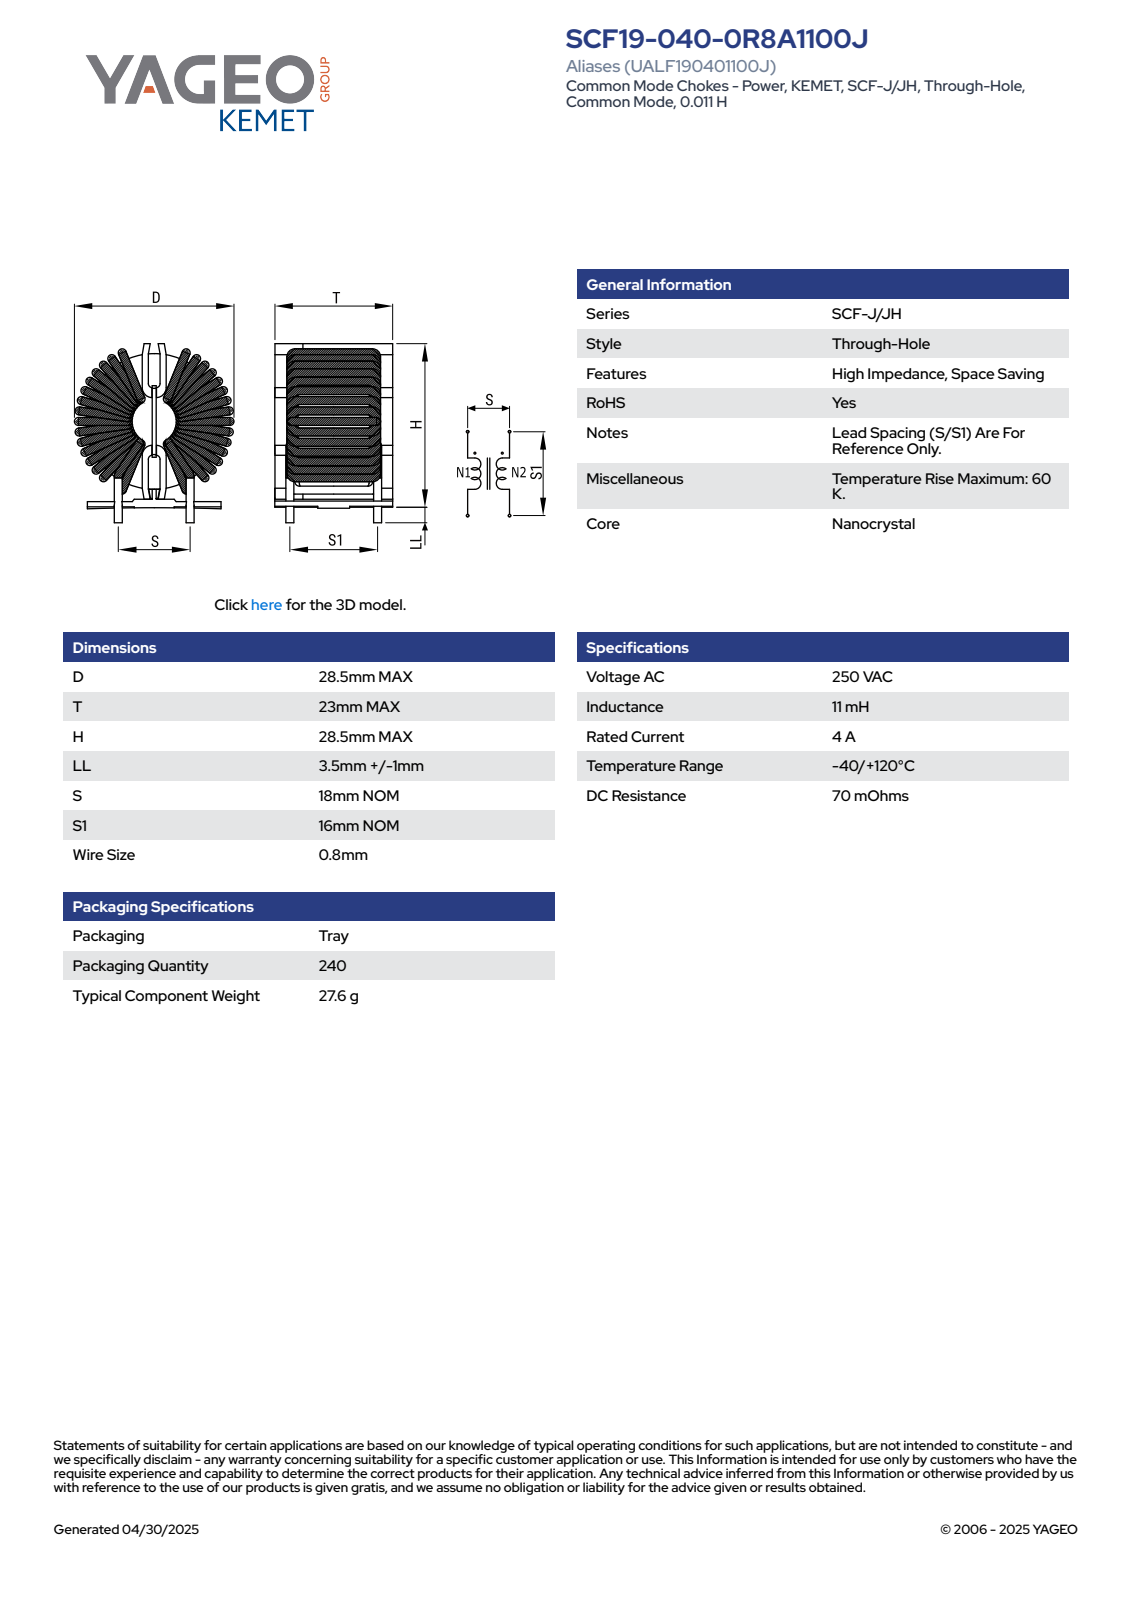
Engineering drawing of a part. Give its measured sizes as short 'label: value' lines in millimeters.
name: SCF19-040-0R8A1100J
written by: SolidWorks 2018 (AUTOMOTIVE_DESIGN)
unit: mm
bodies: 1 solid, 489 faces (274 planar, 125 cylindrical, 90 other)
size: 32 × 28.5 × 23
volume: 11 429 mm³; area: 7 545 mm²
bosses: 10× ⌀0.8
rounds: 24× R0.4, 8× R0.5, 4× R0.1, 4× R0.2, 2× R1.75, 1× R4.88, 1× R5.43, 1× R6.3
face distances: 1, 23, 1.5, 2, 1.15, 0.85, 1.48, 21.52, 1.05, 0.5
